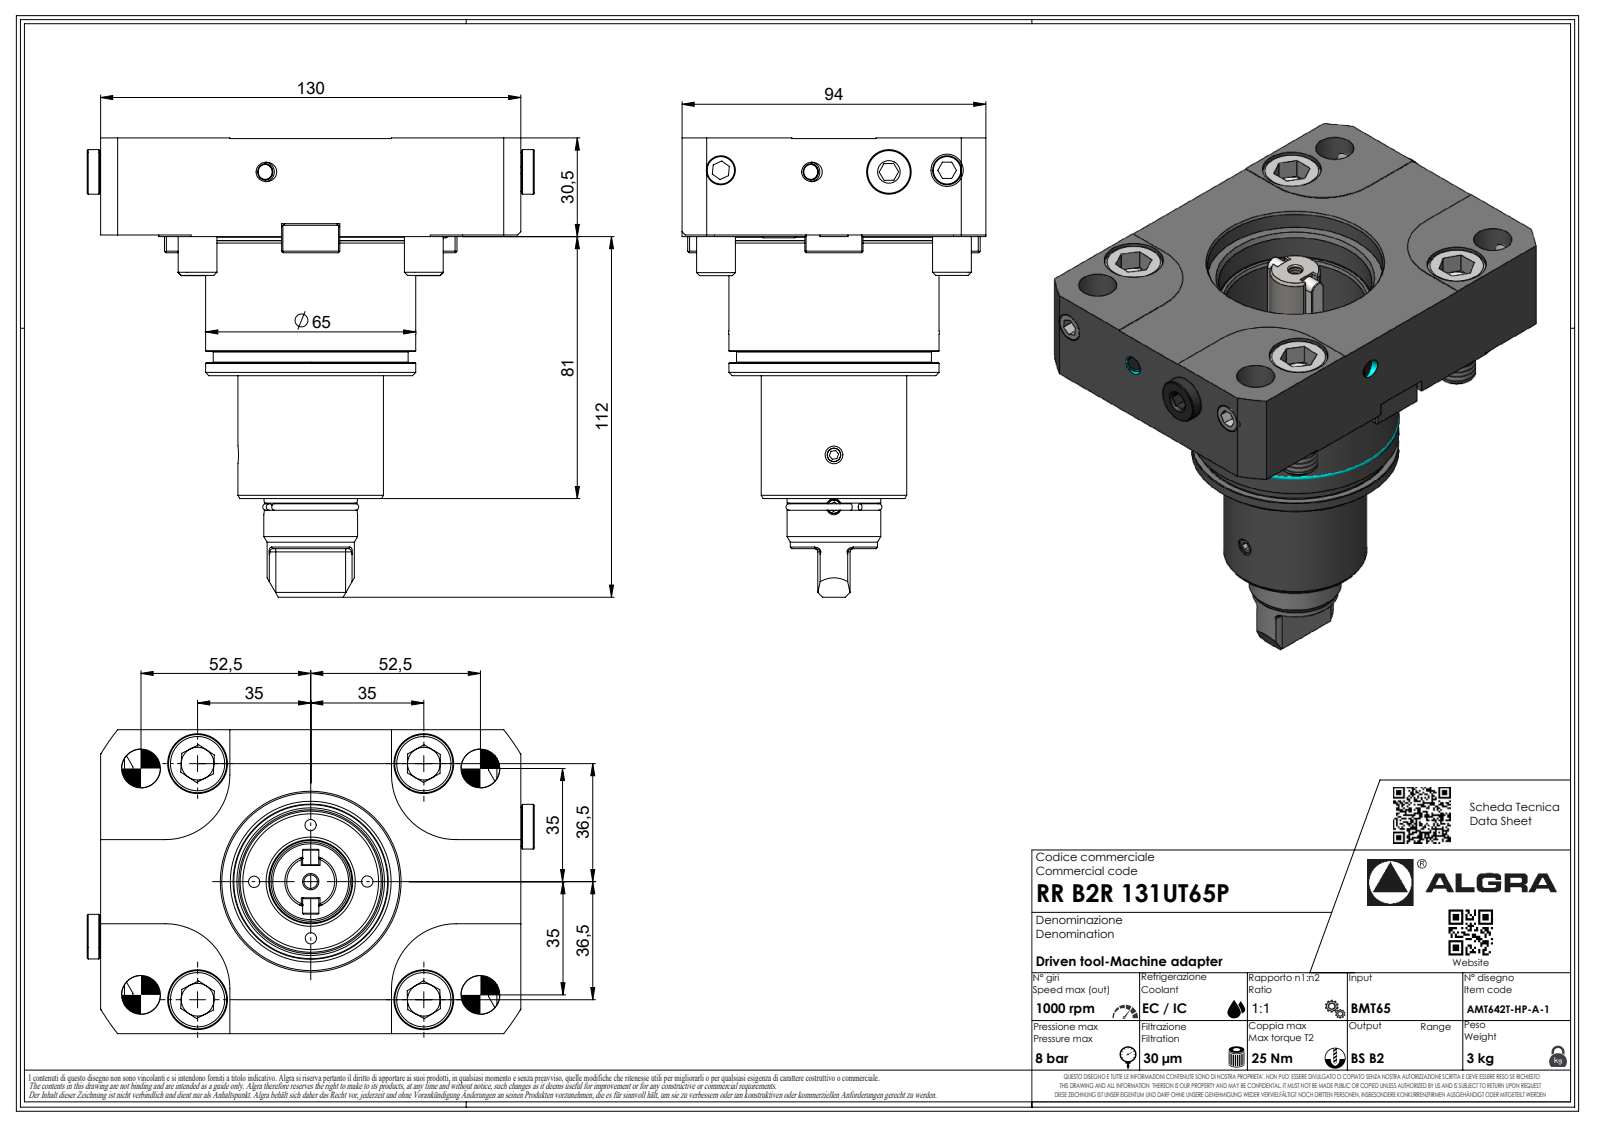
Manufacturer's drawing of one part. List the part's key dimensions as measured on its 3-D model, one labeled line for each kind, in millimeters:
Part name (STEP PRODUCT): RRB2R131UT65P
STEP written by: SolidWorks 2023 (AUTOMOTIVE_DESIGN)
Units: millimetres
Bodies: 1 solid, 396 faces (247 planar, 52 cylindrical, 97 other)
Overall size (bounding box): 142 × 130 × 94
Volume: 581 877 mm³ · Surface area: 54 804 mm²
Round holes (diameter × count): ⌀2.1 ×1
Round bosses / shafts (diameter × count): ⌀65 ×1, ⌀64.6 ×1, ⌀60.3 ×1, ⌀45 ×1, ⌀29 ×1, ⌀27 ×1, ⌀6.37 ×1, ⌀1.7 ×1
Partial cylindrical surfaces — rounded edges, fillets, slot ends (radius × count): R0.33 ×7, R0.52 ×7, R3.7 ×7, R1 ×6, R10 ×4, R20 ×4, R0.21 ×1, R76 ×1
Main face-to-face distances: 30.3, 30.5, 94, 0.5, 29.8, 30, 130, 43, 43.5, 73.3
